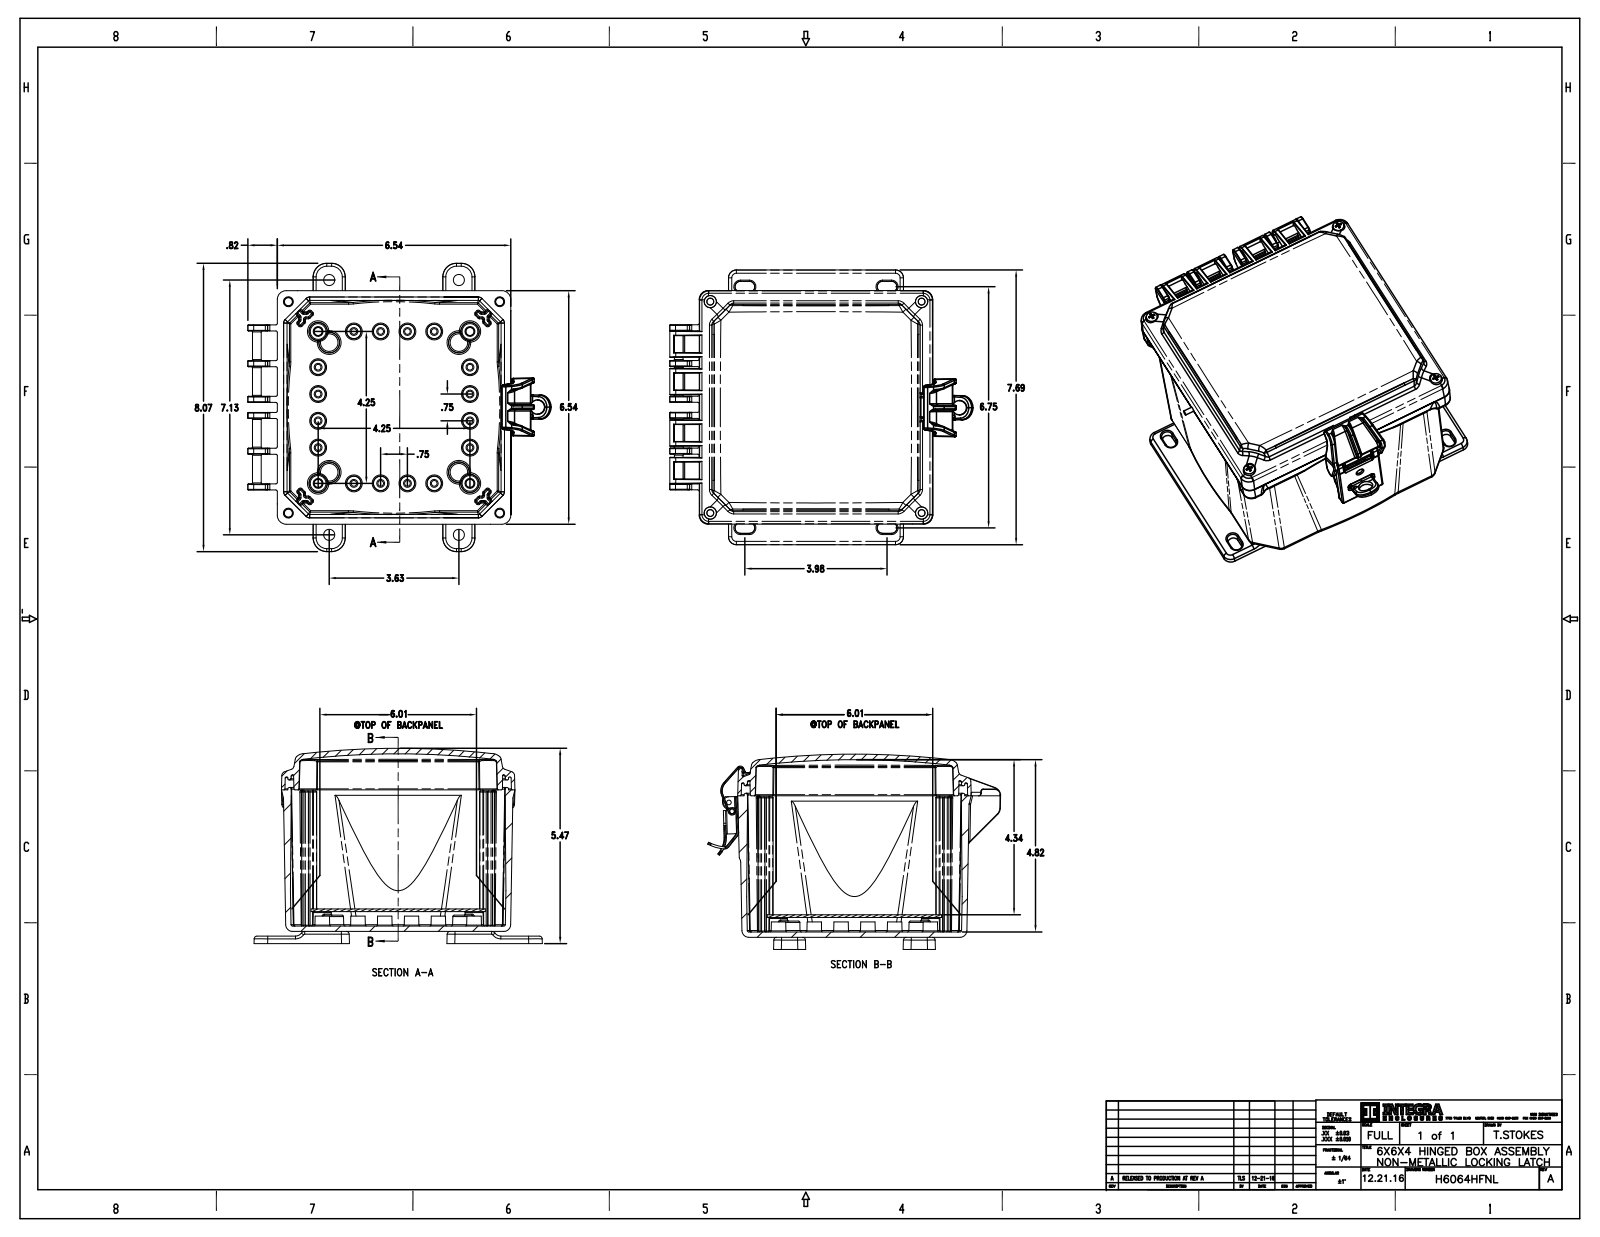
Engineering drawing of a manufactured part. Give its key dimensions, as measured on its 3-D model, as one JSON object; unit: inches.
{"part_name": "H664BH; 9912525-80-10; 9912521-80-10; H664BH_ASM (+8 more)", "step_written_by": "CREO PARAMETRIC BY PTC INC, 2016050 (CONFIG_CONTROL_DESIGN)", "units": "inches", "bodies": {"solids": 31, "faces": 6261, "planar": 2583, "cylindrical": 1910, "other": 1768}, "overall_size": [8.487, 7.69, 5.465], "volume_in3": 40.81, "surface_area_in2": 576.1, "round_holes": [[0.16, 16], [0.19, 8], [0.201, 4], [0.116, 2], [0.125, 2], [0.08, 1], [0.14, 1], [0.175, 1], [0.21, 1], [0.33, 1], [0.35, 1], [0.4, 1]], "round_bosses_or_shafts": [[0.25, 12], [0.3, 8], [0.298, 8], [0.29, 8], [0.26, 8], [0.258, 8], [0.375, 4], [0.372, 4]], "partial_cylinders_radius": [[0.03, 431], [0.02, 99], [0.015, 74], [0.025, 64], [0.005, 48], [0.04, 43], [0.09, 40], [0.1, 28]], "face_to_face_distances": [0.15, 0.49, 0.12, 3.81, 0.34, 3.96, 0.392, 0.22, 4.3, 5.694], "hole_center_spacings": [4.25, 4.315, 4.596, 0.75, 0.757, 1, 1.473, 1.5]}
